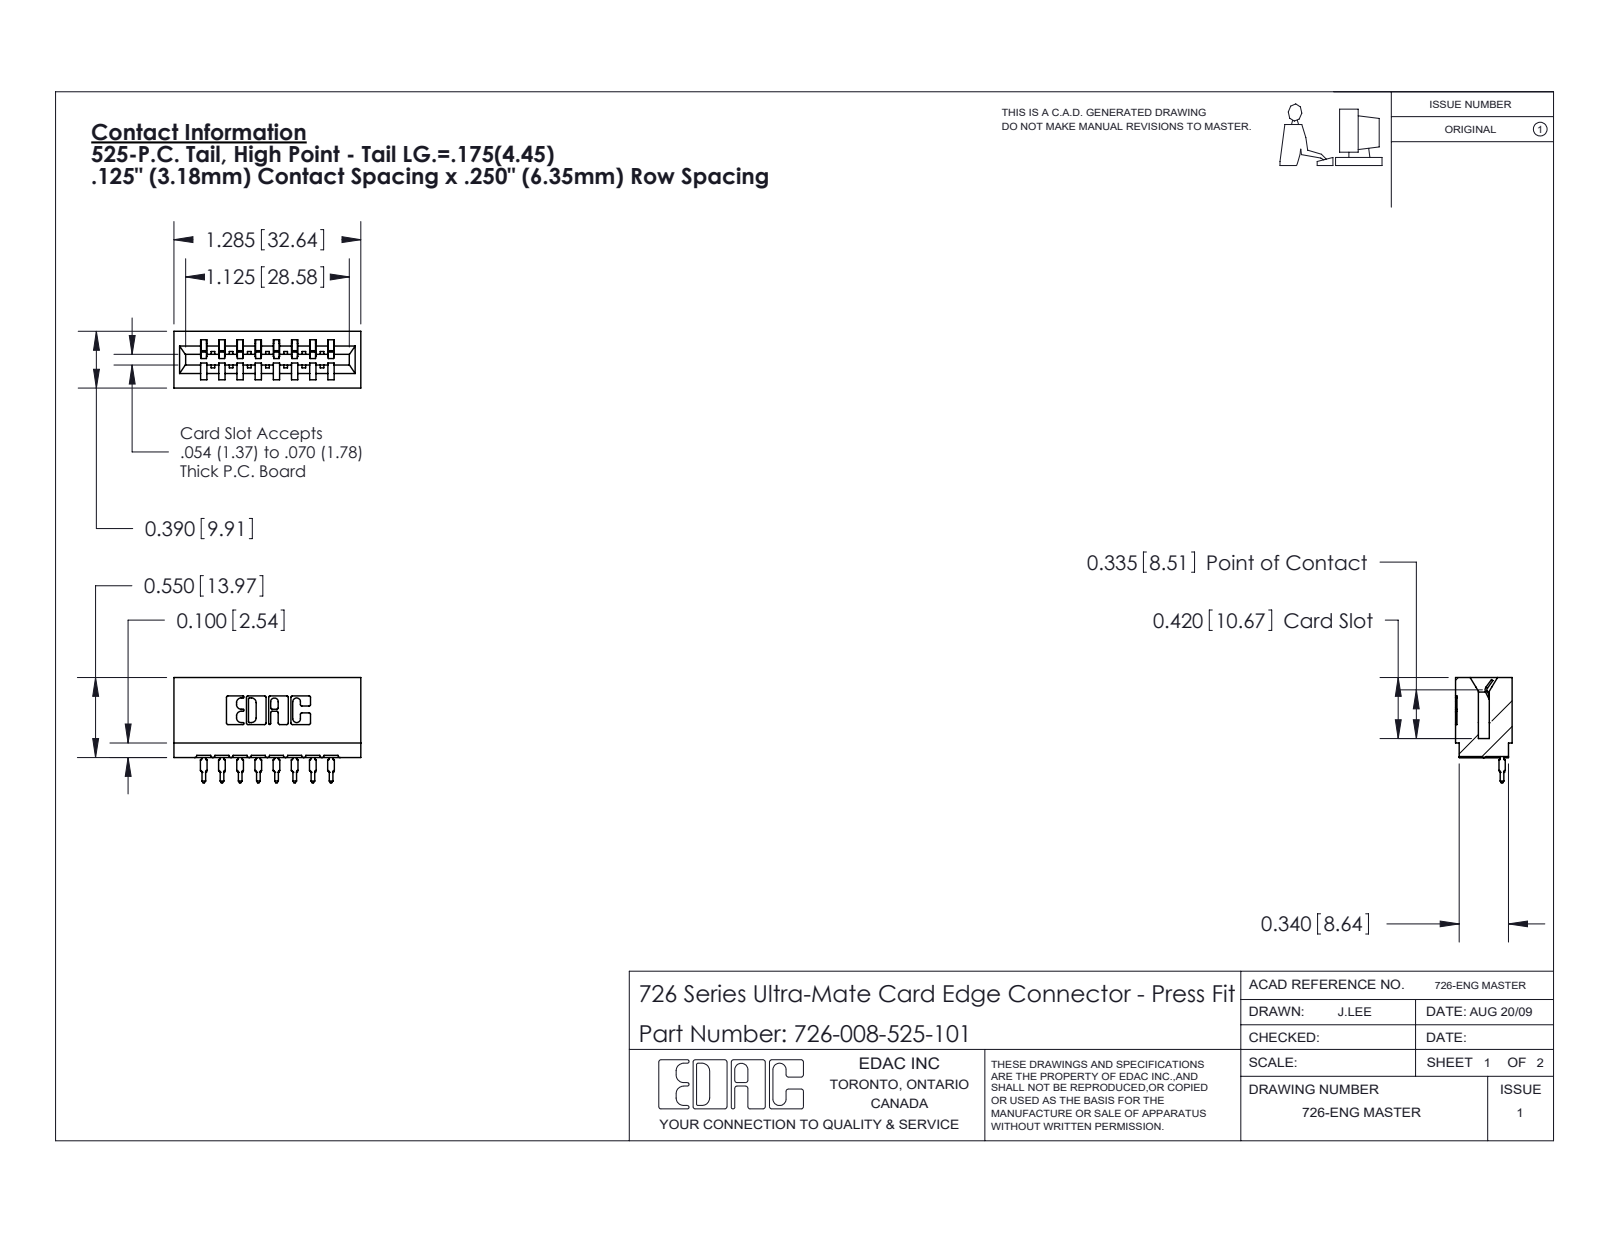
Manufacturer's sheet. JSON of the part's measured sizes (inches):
{"part_name": "746-292-001_525; 726 Part_.515 Slot Depth - 01; 726-008-525-101", "step_written_by": "SolidWorks 2020 (CONFIG_CONTROL_DESIGN)", "units": "inches", "bodies": {"solids": 9, "faces": 961, "planar": 559, "cylindrical": 194, "other": 208}, "overall_size": [1.285, 0.724, 0.39], "volume_in3": 0.189, "surface_area_in2": 6.497, "partial_cylinders_radius": [[0.01, 22], [0.021, 16], [0.015, 9], [0.007, 6], [0.031, 6], [0.005, 4], [0.011, 4], [0.026, 3]], "face_to_face_distances": [0.25, 0.042, 0.125, 0.5, 0.333, 0.057, 0.208, 0.125, 0.292, 0.375]}
